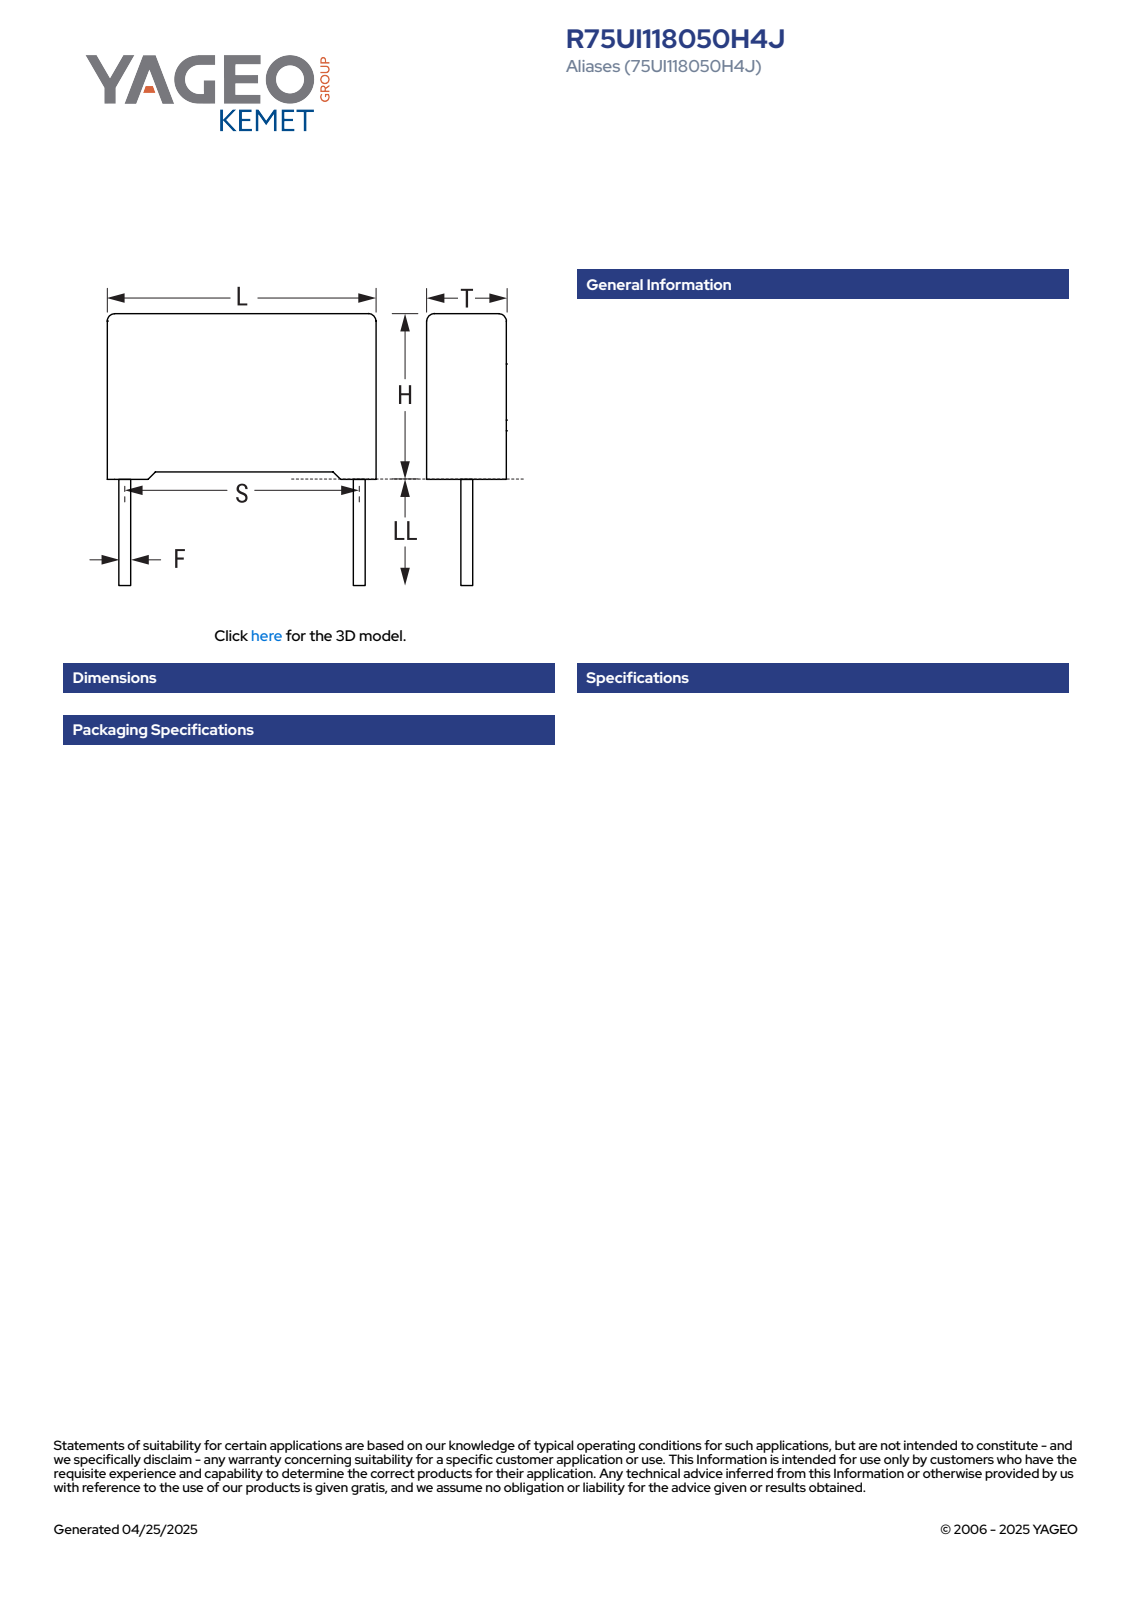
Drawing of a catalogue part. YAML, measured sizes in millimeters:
part_name: "CFR_RB2_18X10X4_L18.3H10.1T4.2S15LL27F0.85"
step_written_by: "SolidWorks 2021 (AUTOMOTIVE_DESIGN)"
units: millimeters
bodies: {solids: 4, faces: 85, planar: 77, cylindrical: 8, other: 0}
overall_size: [37.1, 18.3, 4.21]
volume: 762
surface_area: 786
round_bosses_or_shafts:
  - {diameter: 0.85, count: 2}
partial_cylinders:
  - {radius: 0.5, count: 4}
face_to_face_distances: [4.2, 9.35, 18.3, 0.61, 3.59, 0.4, 9.75, 0.75, 0.35, 10.1]
